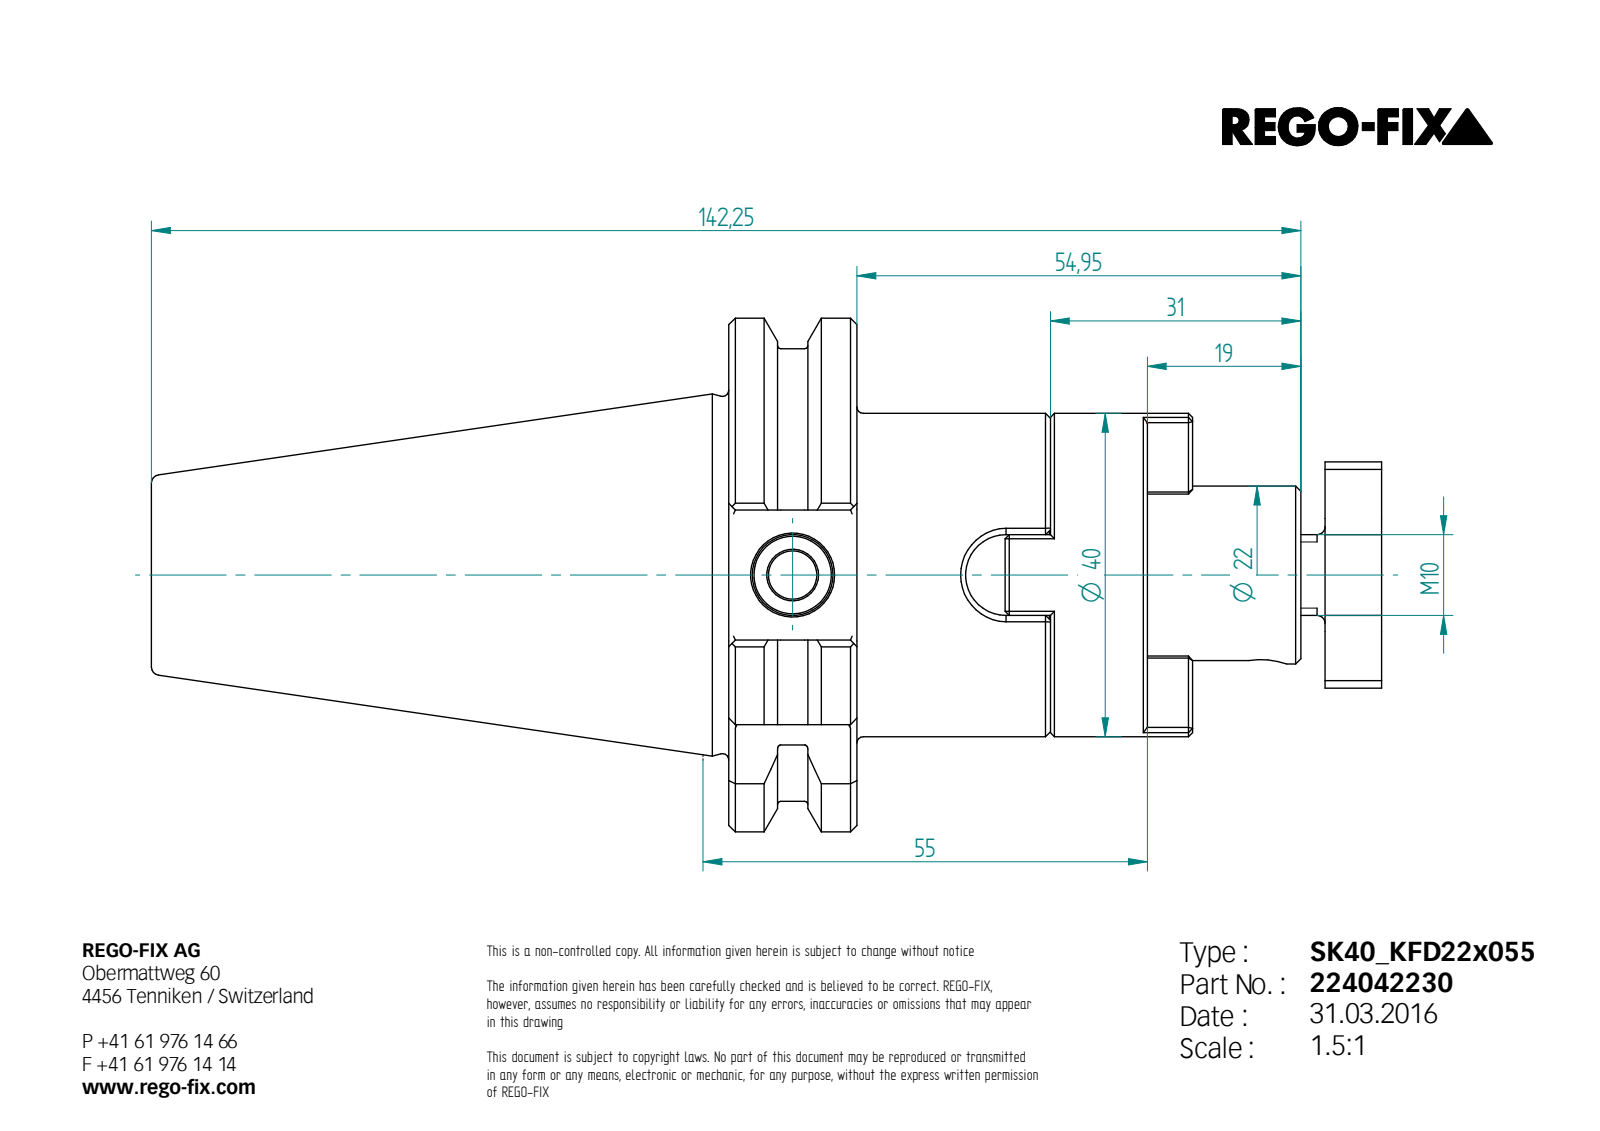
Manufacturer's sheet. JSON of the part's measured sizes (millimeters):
{"step_written_by": "Unknown (AUTOMOTIVE_DESIGN)", "units": "millimeters", "bodies": {"solids": 3, "faces": 239, "planar": 130, "cylindrical": 48, "other": 61}, "overall_size": [152.25, 63.55, 61.01], "volume_mm3": 153238, "surface_area_mm2": 34189, "round_holes": [[6, 1], [8.38, 1], [10, 1], [10.5, 1], [13.84, 1], [17, 1], [22, 1]], "round_bosses_or_shafts": [[40, 1], [21.4, 1], [10, 1]], "partial_cylinders_radius": [[0.5, 13], [2, 4], [3, 2], [5, 1], [14, 1], [28, 1], [31.77, 1]], "face_to_face_distances": [15.85, 39.8, 23.95, 51.8, 35.95, 12, 10, 80.8, 64.95, 41]}
